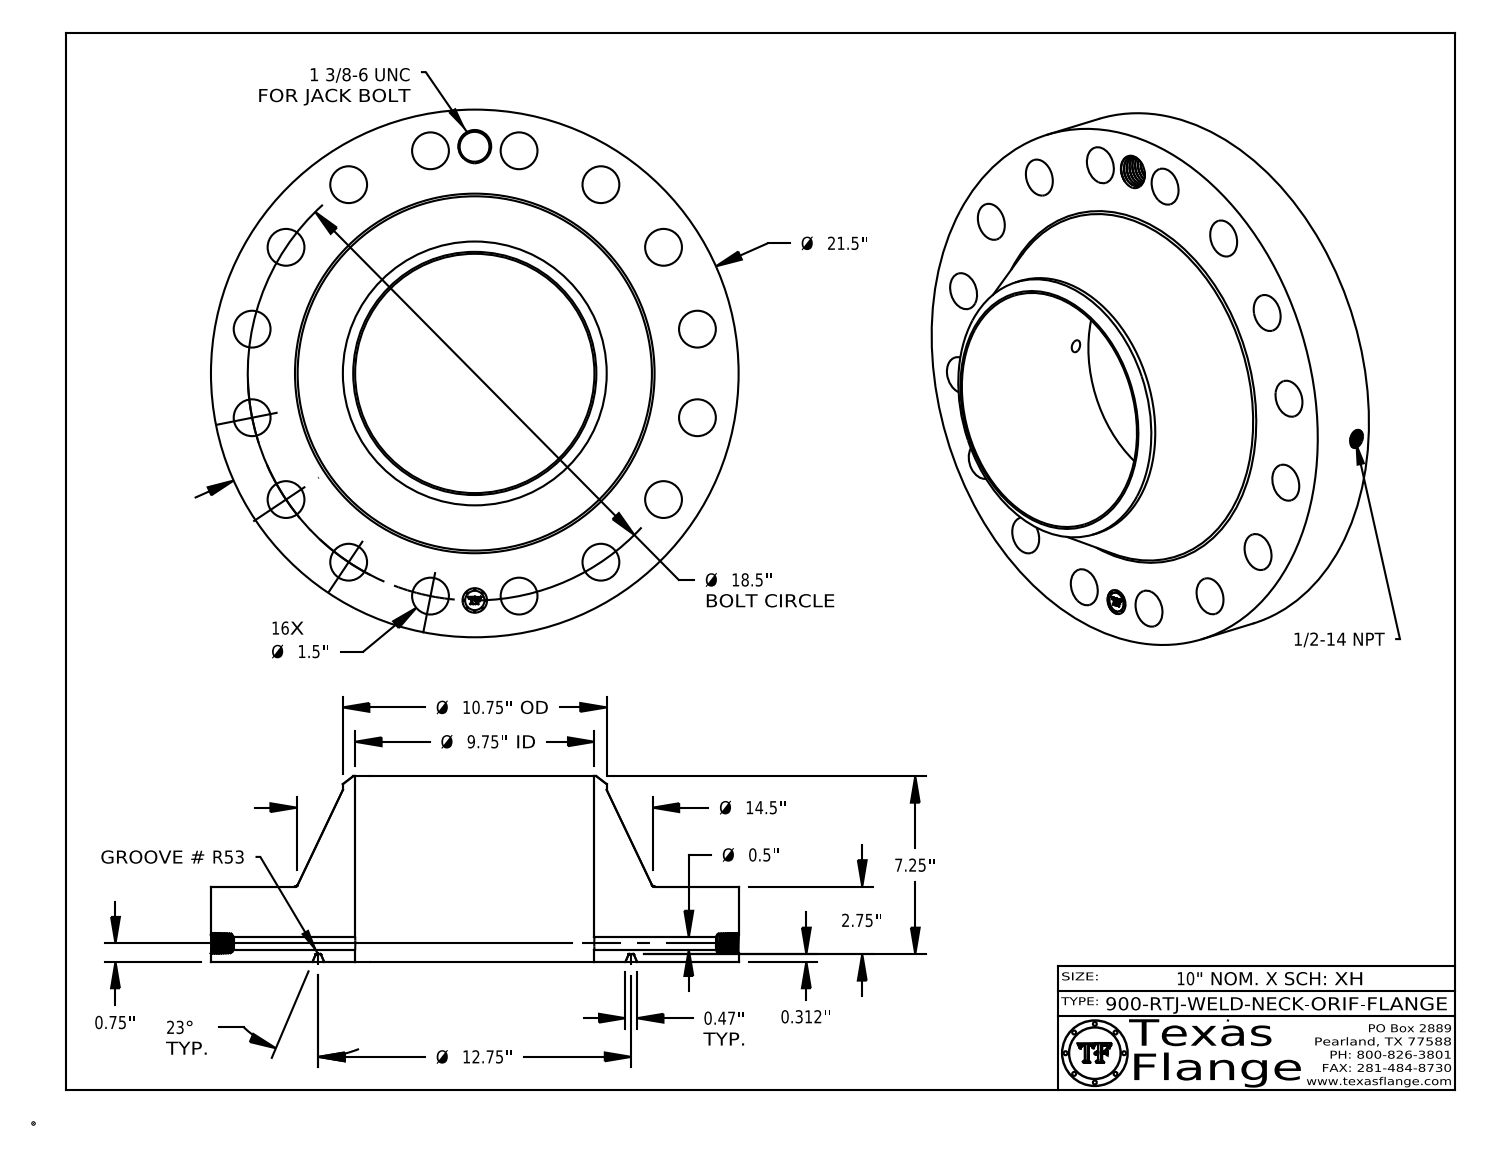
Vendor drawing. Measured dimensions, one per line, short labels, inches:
name: 900-RTJ-WELD-NECK
written by: CATIA V5 STEP AP214 (AUTOMOTIVE_DESIGN)
unit: in
bodies: 1 solid, 813 faces (370 planar, 114 cylindrical, 329 other)
size: 21.5 × 21.5 × 7.562
volume: 995 in³; area: 1 352 in²
holes: 16× ⌀1.5, 1× ⌀0.5, 1× ⌀0.672, 1× ⌀1, 1× ⌀1.219, 1× ⌀9.75
bosses: 8× ⌀0.061, 1× ⌀21.5, 1× ⌀10.75, 1× ⌀0.788
face distances: 3.062, 0.312, 2.75, 7.562, 7.25, 4.5, 3.047, 2.735, 0.015, 4.515
hole spacings: 10.278, 17.092, 3.609, 9.25, 7.08, 7.08, 9.25, 13.081
